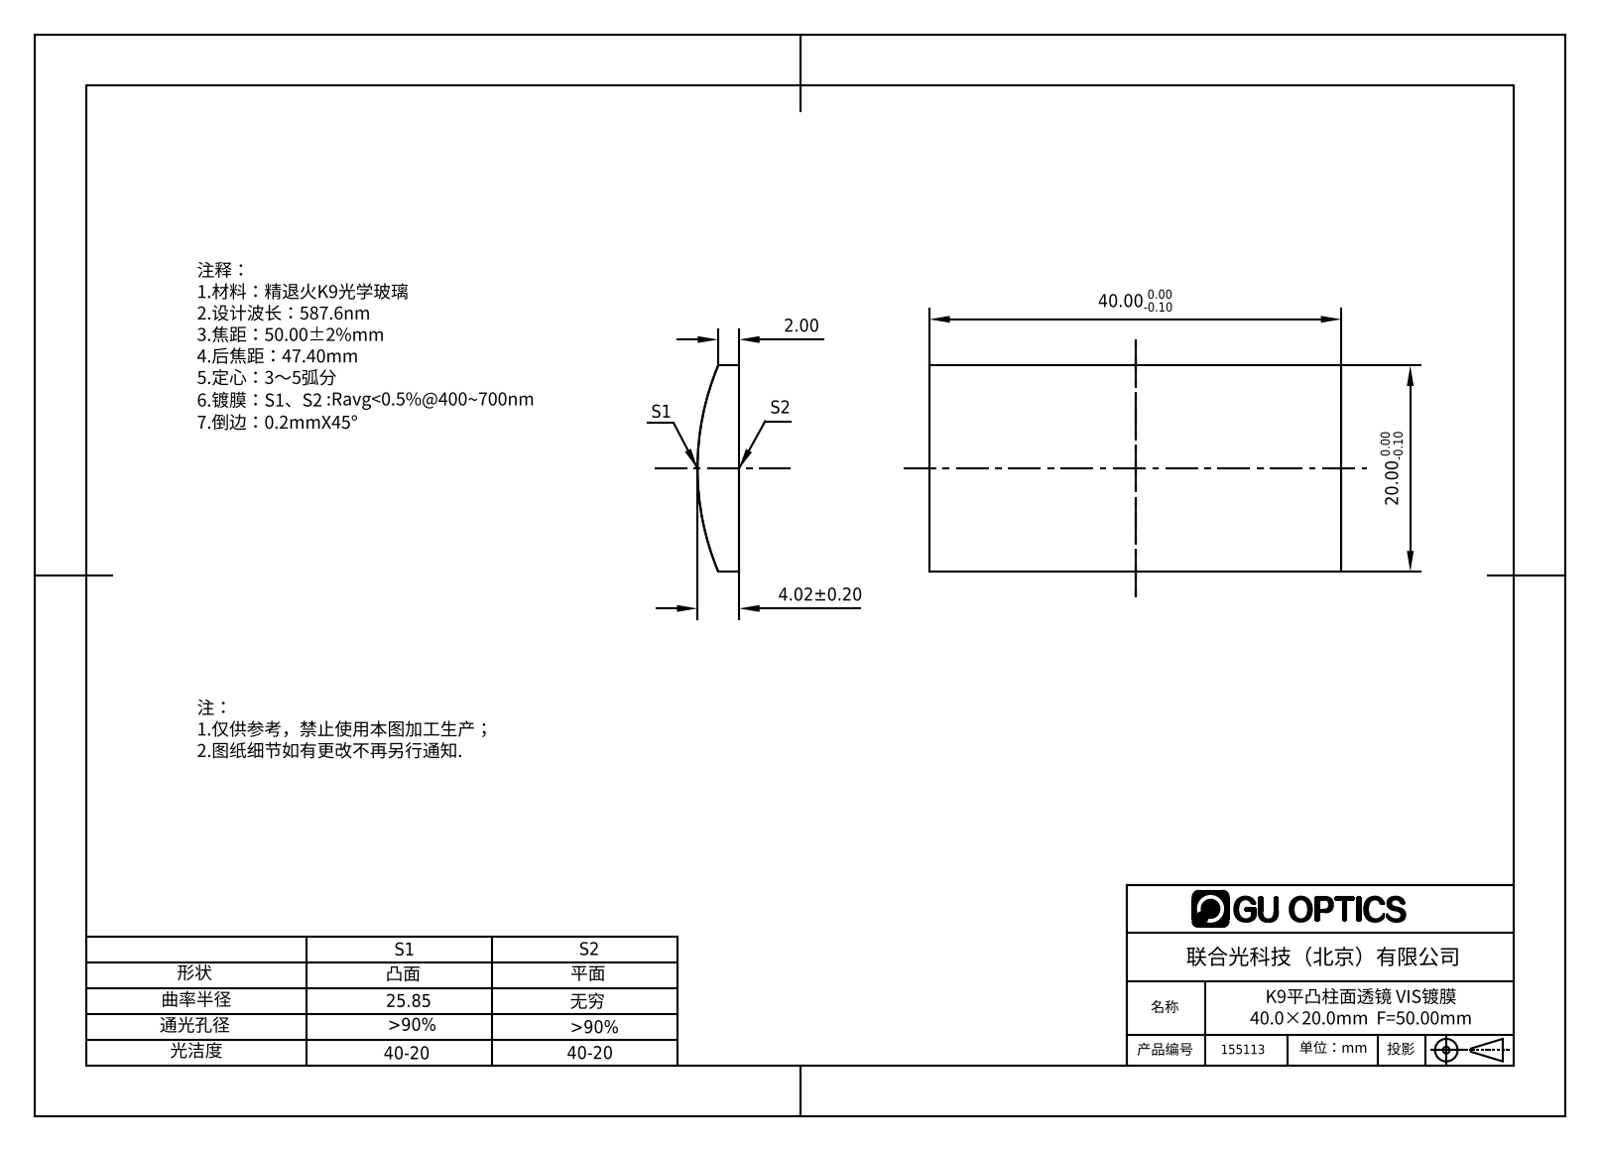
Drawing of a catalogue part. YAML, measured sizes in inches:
part_name: "155047"
step_written_by: "SolidWorks 2016 (AUTOMOTIVE_DESIGN)"
units: inches
bodies: {solids: 1, faces: 6, planar: 5, cylindrical: 1, other: 0}
overall_size: [1.575, 0.787, 0.158]
volume: 0.164
surface_area: 2.97
partial_cylinders:
  - {radius: 1.018, count: 1}
face_to_face_distances: [0.787, 1.575]
